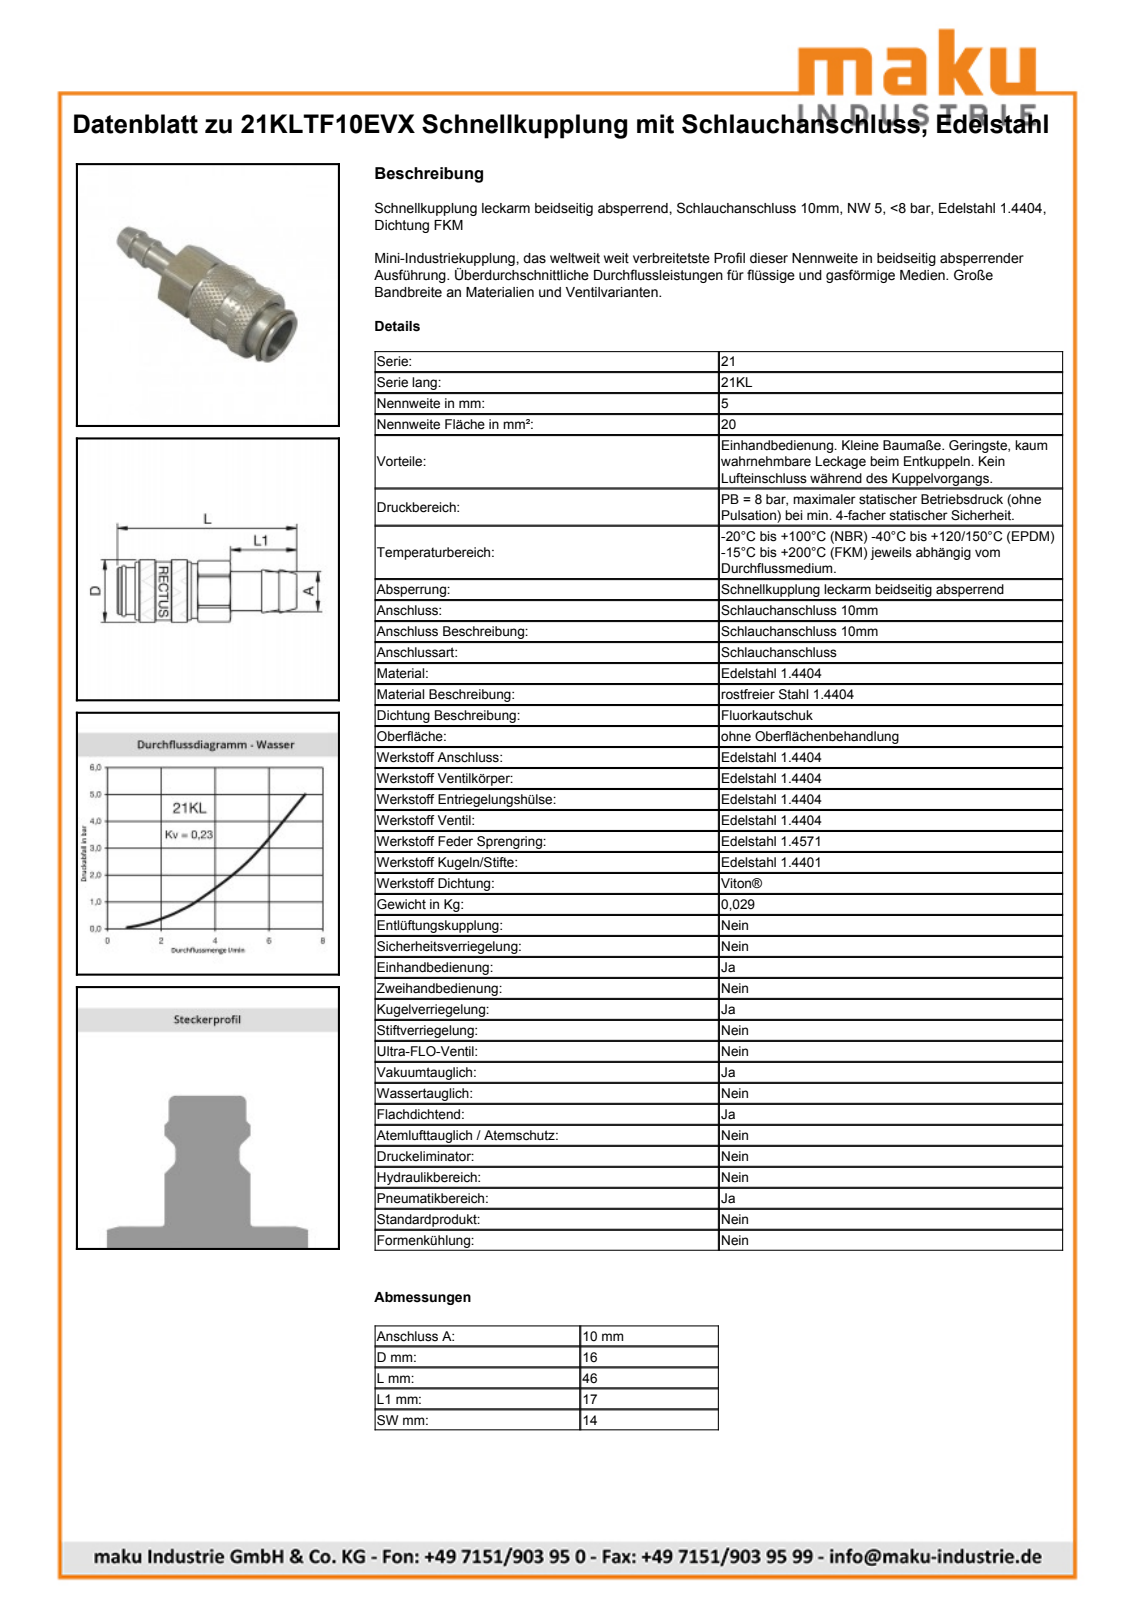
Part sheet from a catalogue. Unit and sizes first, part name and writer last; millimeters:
Units: millimetres
Overall size (bounding box): 46.2 × 16 × 16
Round holes (diameter × count): ⌀9.5 ×1, ⌀10.45 ×1, ⌀11.5 ×1, ⌀12.15 ×1, ⌀12.75 ×1, ⌀14 ×1, ⌀14.6 ×1
Round bosses / shafts (diameter × count): ⌀16 ×1, ⌀15 ×1, ⌀13.8 ×1, ⌀12 ×1, ⌀11.3 ×1, ⌀11.2 ×1, ⌀10.05 ×1
Partial cylindrical surfaces — rounded edges, fillets, slot ends (radius × count): R7.4 ×1, R7.9 ×1
Main face-to-face distances: 14, 5.14, 29.2, 24.06, 46.2, 41.06, 17, 1, 14.5, 16.2
Volume: 5 844 mm³ · Surface area: 4 441 mm²
Bodies: 1 solid, 357 faces (129 planar, 51 cylindrical, 177 other)
Part name (STEP PRODUCT): D113134
STEP written by: Autodesk Inventor 2013 (AUTOMOTIVE_DESIGN)
